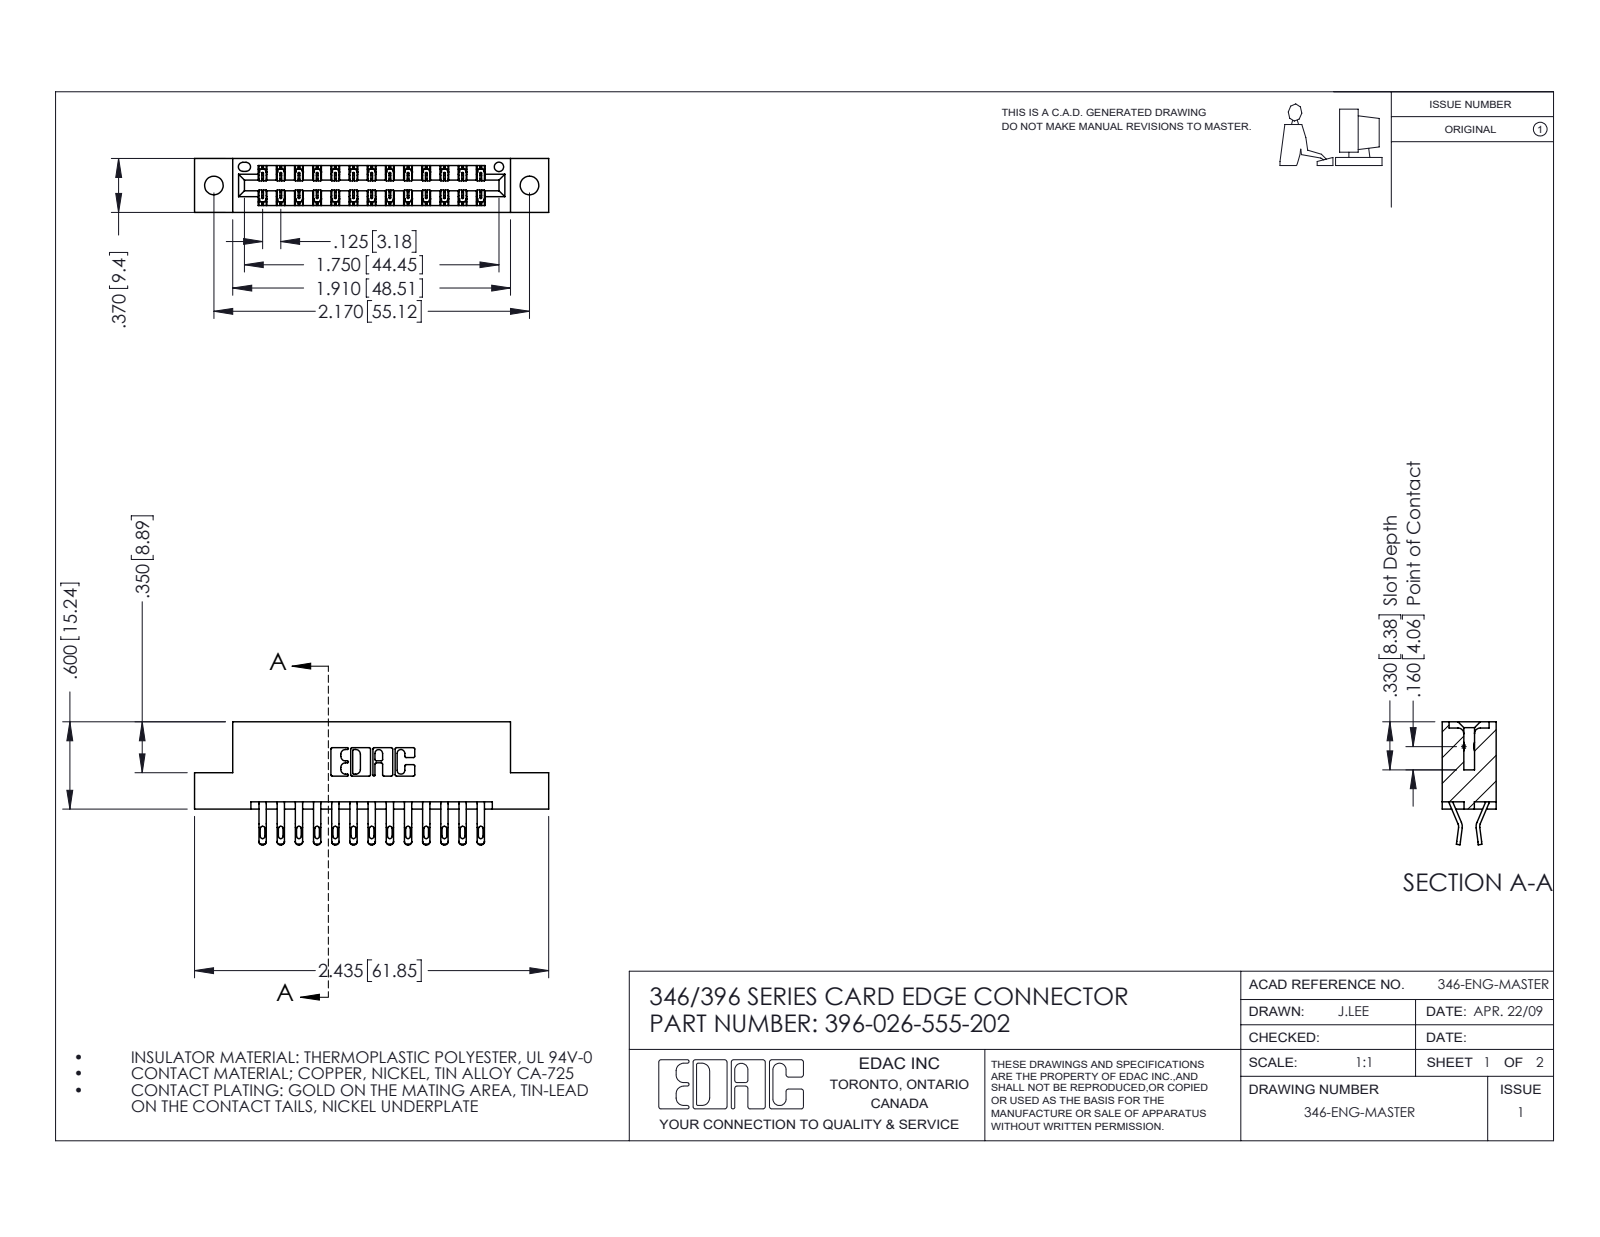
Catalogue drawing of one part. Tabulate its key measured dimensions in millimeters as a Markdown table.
| quantity | value |
| --- | --- |
| part name | 346 Part_Flush Mounting Lugs - 0.128 Dia; 396-026-555-202; 345-292-001_555 Tail |
| STEP written by | SolidWorks 2016 (CONFIG_CONTROL_DESIGN) |
| units | millimeters |
| bodies | 27 solids, 1630 faces (934 planar, 696 cylindrical, 0 other) |
| overall size | 61.8 × 21.5 × 9.4 |
| volume | 5 850 mm³ |
| surface area | 7 581 mm² |
| round holes (diameter × count) | 3.3 × 2, 1.6 × 1 |
| partial cylindrical surfaces (radius × count) | 0.4 × 52, 0.5 × 52, 0.2 × 39, 0.3 × 22, 0.2 × 6, 0.8 × 6, 0.7 × 3, 0.3 × 2 |
| main face-to-face distances | 6.4, 1.2, 8.2, 9.4, 0.6, 1.8, 7.6, 7, 3.8, 5.6 |
| hole center spacings | 6.2, 49.9, 55.1 |
